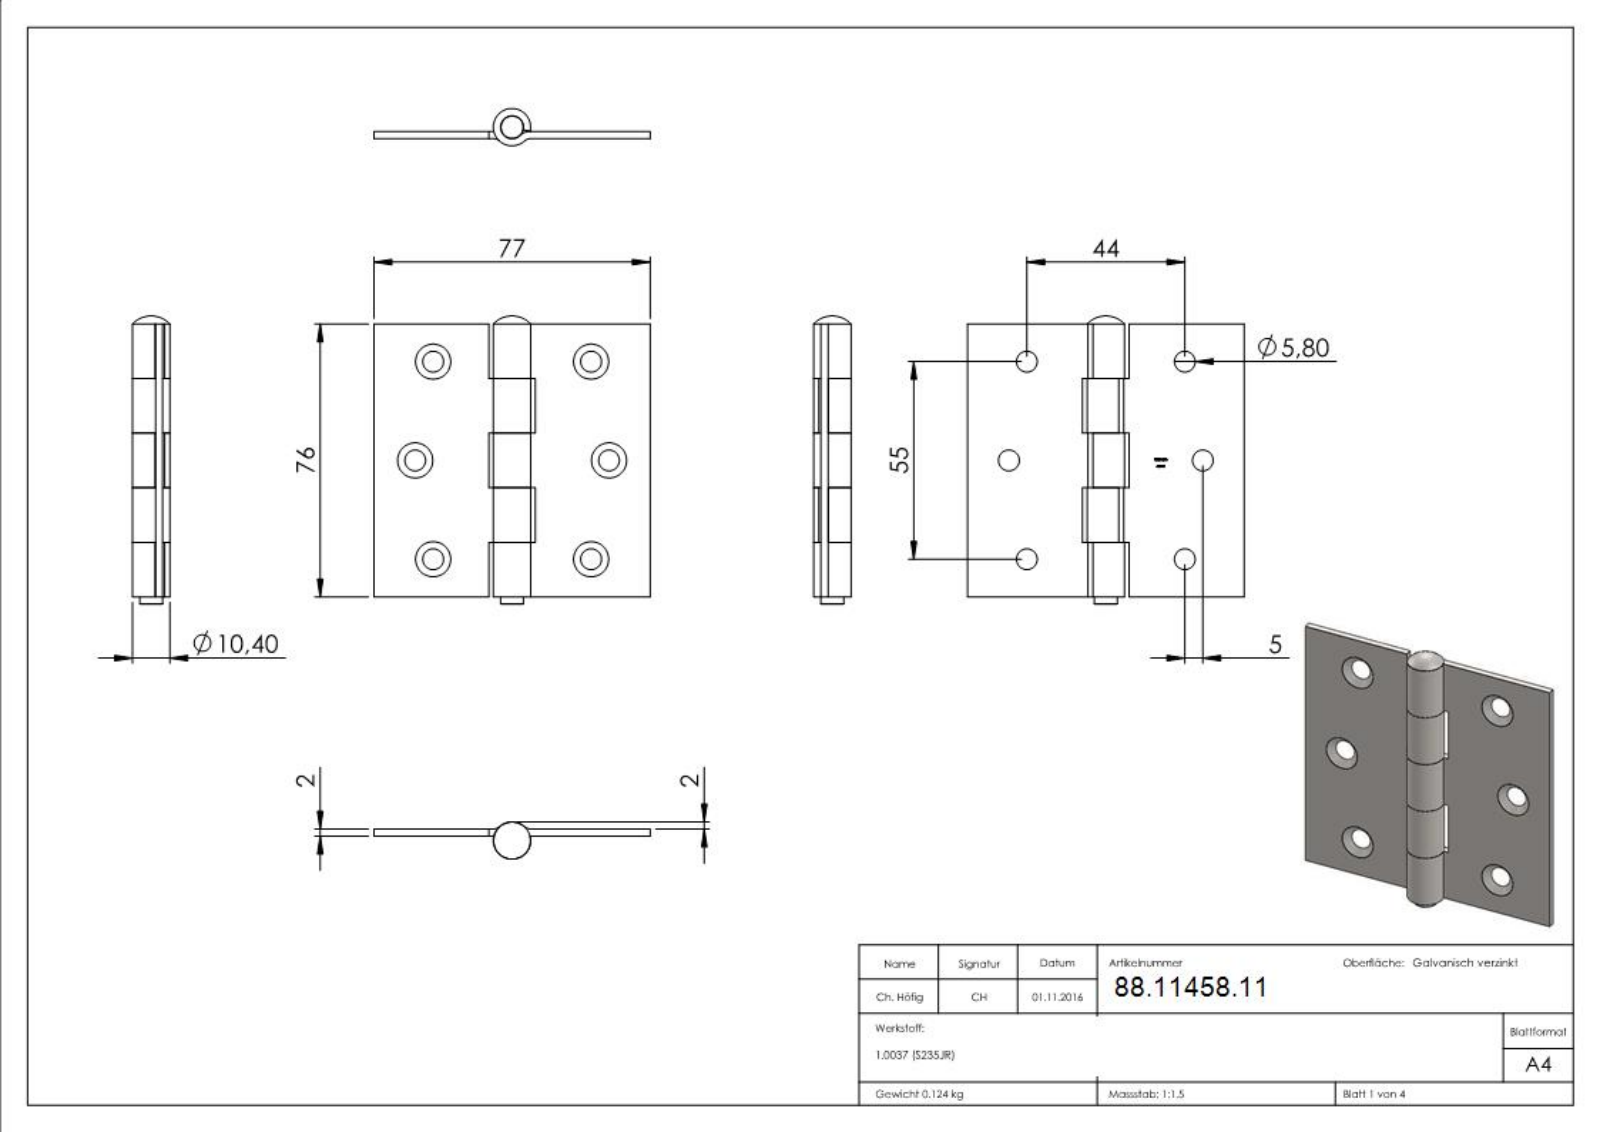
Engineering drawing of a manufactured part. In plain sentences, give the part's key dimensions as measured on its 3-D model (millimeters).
The part is named "458-11 Teil2; 458-11 Teil1; 458-11; 458-11 Teil3". Its 3-D file was written by "SolidWorks 2018 (CONFIG_CONTROL_DESIGN)". It is 3 solids with 241 faces: 139 planar, 21 cylindrical and 81 other. Overall it measures 80.2 by 77 by 10.4 millimeters. Its volume is 15 960 cubic millimeters and its surface area 16 914 square millimeters. Round holes: 1 of diameter 6.4. Round bosses or shafts: 1 of diameter 10.4. Partial cylindrical surfaces (rounded edges, fillets, slot ends): 2 of radius 2, 2 of radius 4. The main face-to-face distances are 2, 15.2, 30.4, 45.6, 60.8, 76, 77, 32, 45, 13.
